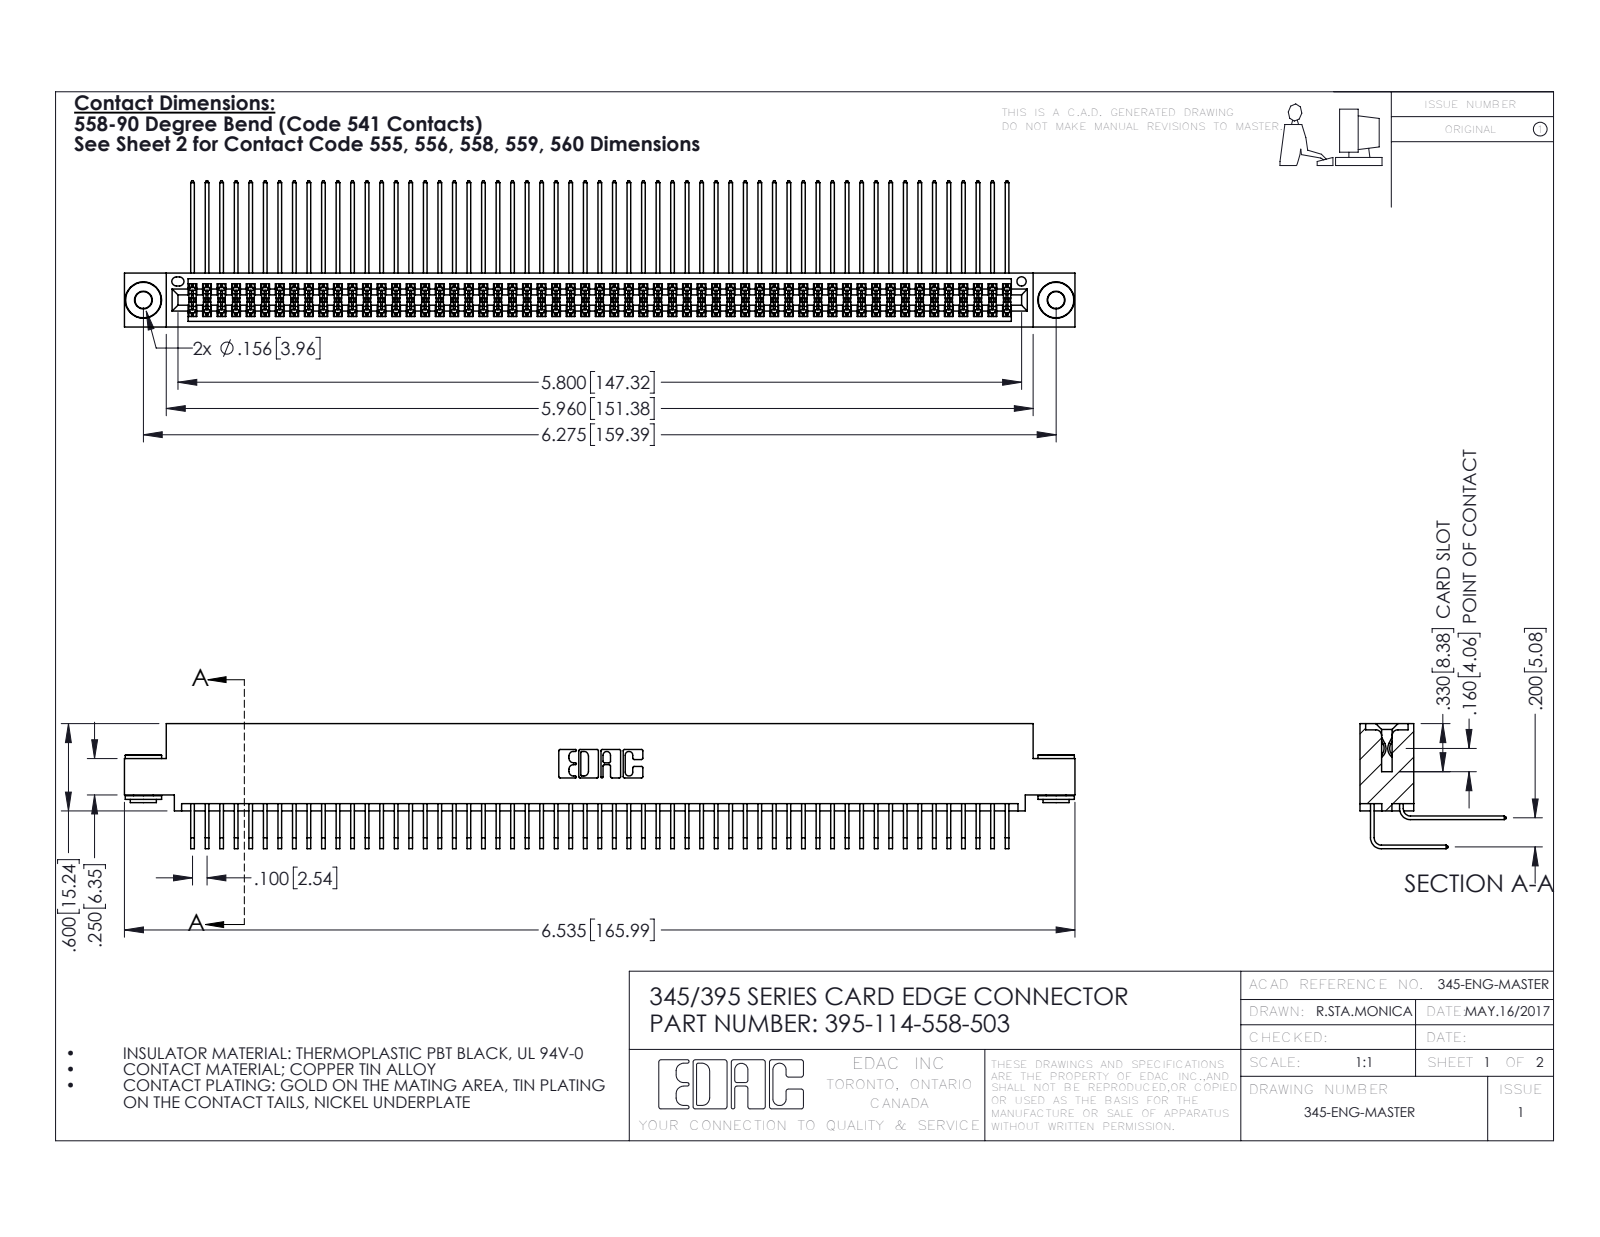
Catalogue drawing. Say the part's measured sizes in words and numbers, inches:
The part is named "345-292-001_558 Tail - 2; 345 Part_0.110 Offset - 0.156 Dia-TH; 345-250-002_345-250-002-102; 345-292-001_558 559 Tail - 1 (+1 more)". Its 3-D file was written by "SolidWorks 2016 (CONFIG_CONTROL_DESIGN)". It is 117 solids with 6096 faces: 4084 planar, 2004 cylindrical and 8 other. Overall it measures 6.535 by 1.005 by 0.859 inches. Its volume is 1.029 cubic inches and its surface area 44.35 square inches. Round holes: 2 of diameter 0.116, 2 of diameter 0.156, 1 of diameter 0.064. Round bosses or shafts: 2 of diameter 0.25, 2 of diameter 0.18, 2 of diameter 0.136. Partial cylindrical surfaces (rounded edges, fillets, slot ends): 172 of radius 0.006, 22 of radius 0.01, 6 of radius 0.007, 6 of radius 0.031, 3 of radius 0.026, 2 of radius 0.014, 2 of radius 0.019, 2 of radius 0.022. The main face-to-face distances are 0.072, 0.298, 0.2, 0.025, 0.37, 0.098, 0.272, 0.225, 0.025, 0.175. The hole center spacings are 0.27, 6.039, 6.275.
